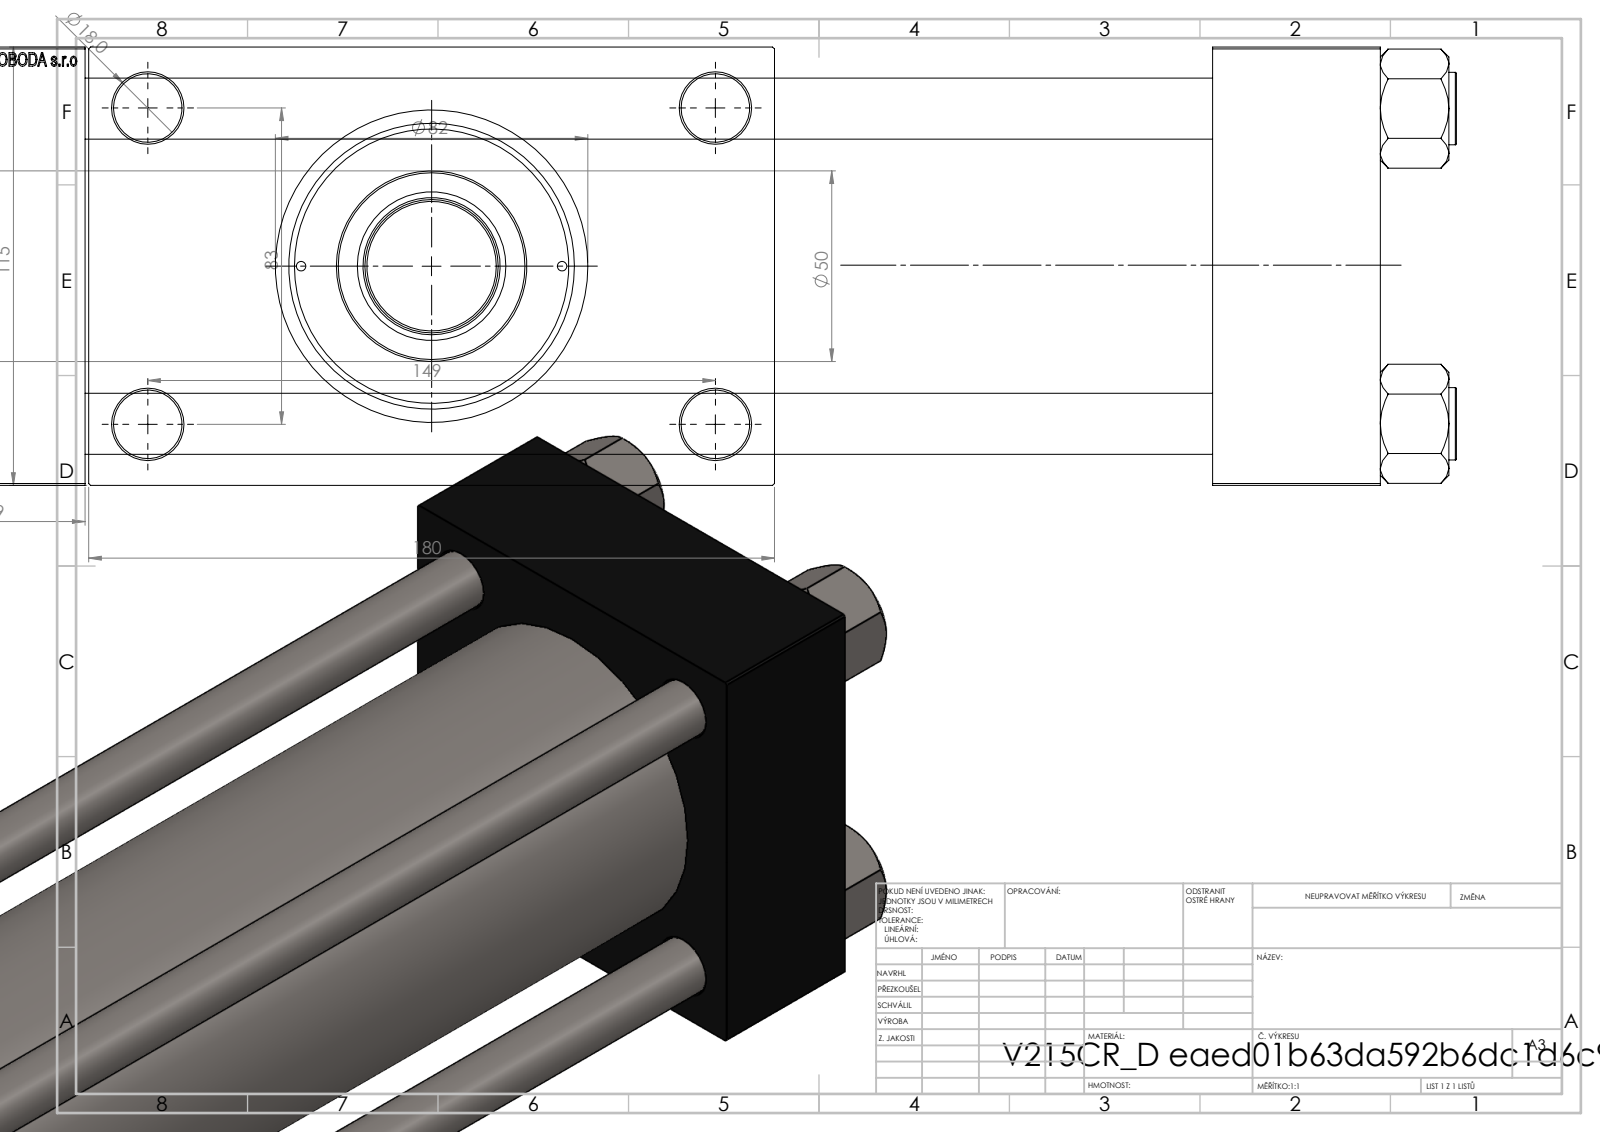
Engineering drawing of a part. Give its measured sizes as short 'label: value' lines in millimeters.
name: V215_VC_A; V215CR_D_Body; V215CR_ROD_END_F; NUT_M5_D (+2 more)
written by: SolidWorks 2019 (CONFIG_CONTROL_DESIGN)
unit: mm
bodies: 12 solids, 1174 faces (551 planar, 97 cylindrical, 526 other)
size: 496 × 180 × 115
volume: 2 619 000 mm³; area: 491 550 mm²
holes: 4× ⌀16, 4× ⌀18, 2× ⌀2.5, 2× ⌀7, 2× ⌀26.44, 2× ⌀35, 1× ⌀25.5, 1× ⌀36, 1× ⌀39, 1× ⌀61, 1× ⌀72, 1× ⌀80
bosses: 4× ⌀19, 1× ⌀86, 1× ⌀82, 1× ⌀50, 1× ⌀35, 1× ⌀21
face distances: 115, 296, 49, 345, 44, 340, 389, 32.5, 147.5, 180
hole spacings: 33.15, 41.96, 57.81, 58.48, 82.7, 85.28, 86.17, 89.24
